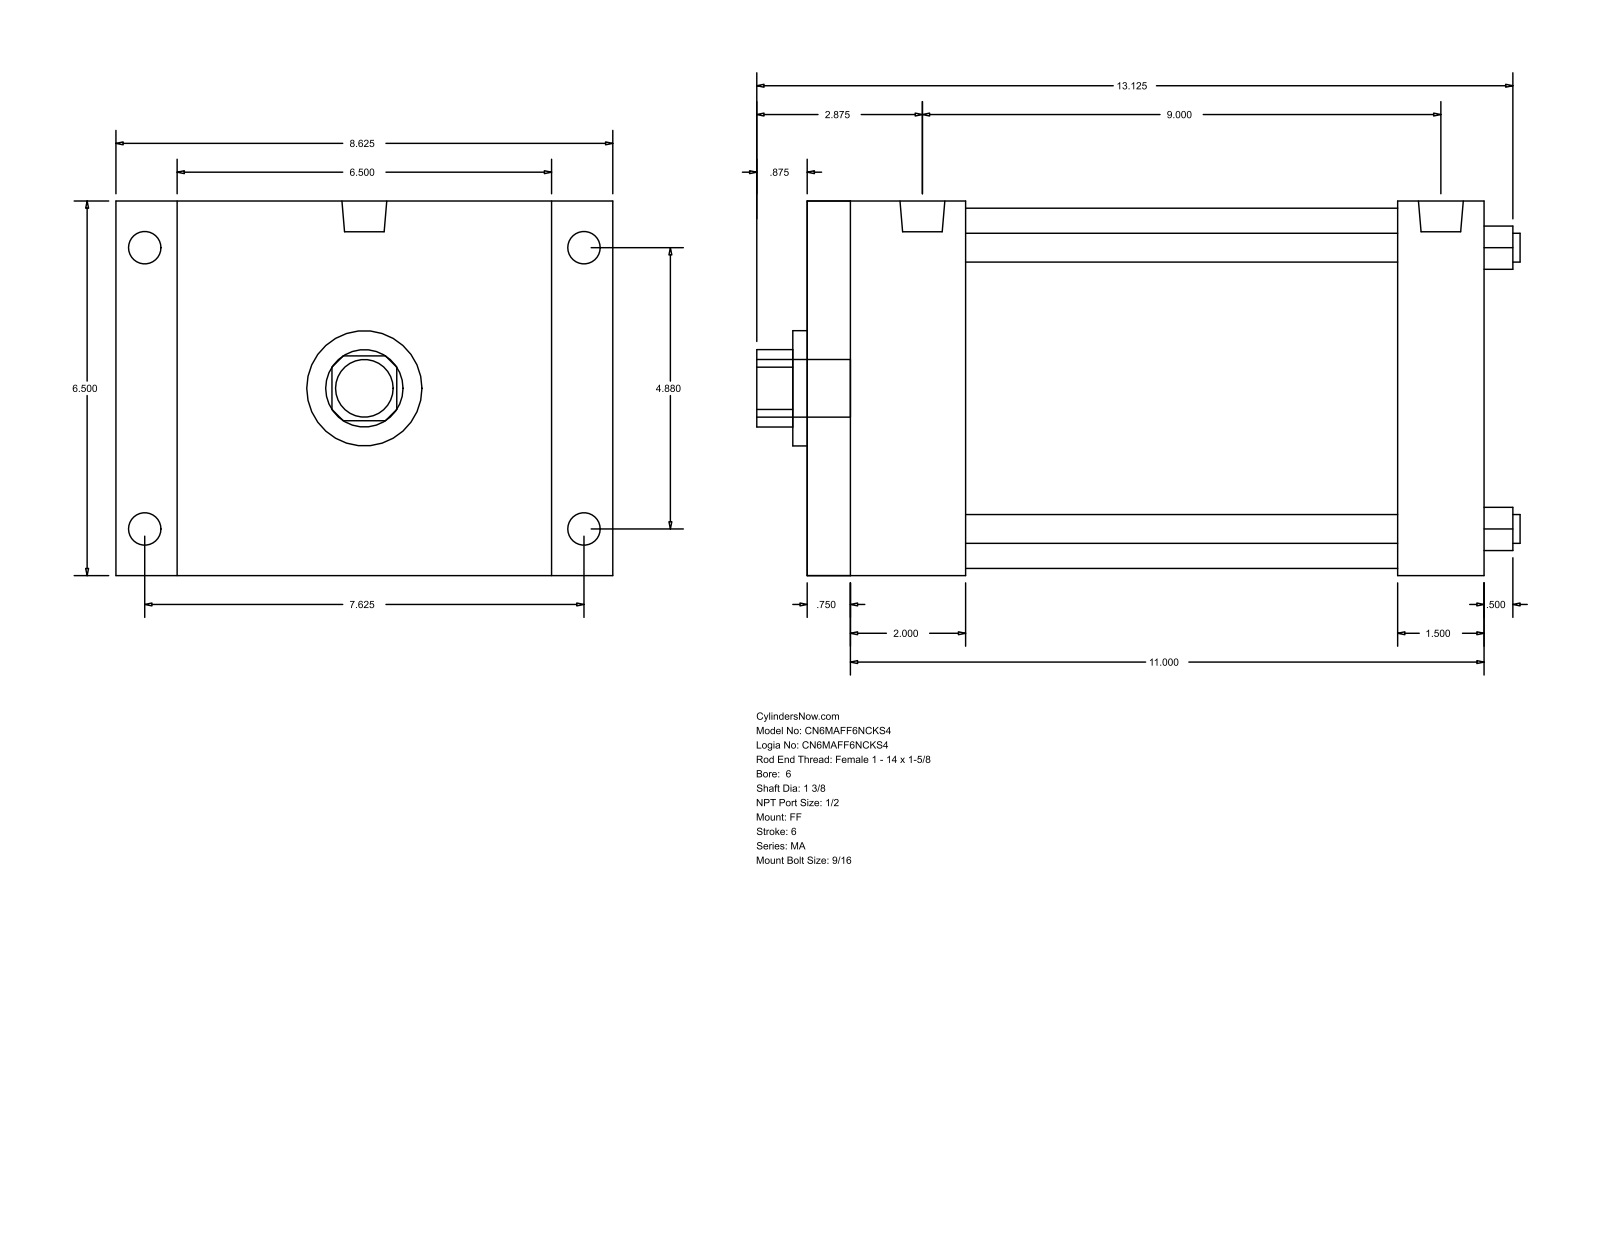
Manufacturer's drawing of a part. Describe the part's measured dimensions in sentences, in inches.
The part is named "MA_FF__0600_1.375". Its 3-D file was written by "GSSL Pune (CONFIG_CONTROL_DESIGN)". It is 0 solids with 92 faces: 64 planar, 28 cylindrical and 0 other. Overall it measures 13.25 by 8.625 by 6.5 inches. Round holes: 4 of diameter 0.5, 1 of diameter 1.375, 1 of diameter 2, 1 of diameter 6.25. Round bosses or shafts: 4 of diameter 0.687, 4 of diameter 0.563, 2 of diameter 0.778, 1 of diameter 1. Partial cylindrical surfaces (rounded edges, fillets, slot ends): 1 of radius 0.672. The main face-to-face distances are 6.5, 11.75, 0.625, 11.125, 2.625, 2, 9.125, 10.25, 9.625, 7.625. The hole center spacings are 3.451, 4.88, 6.902.
